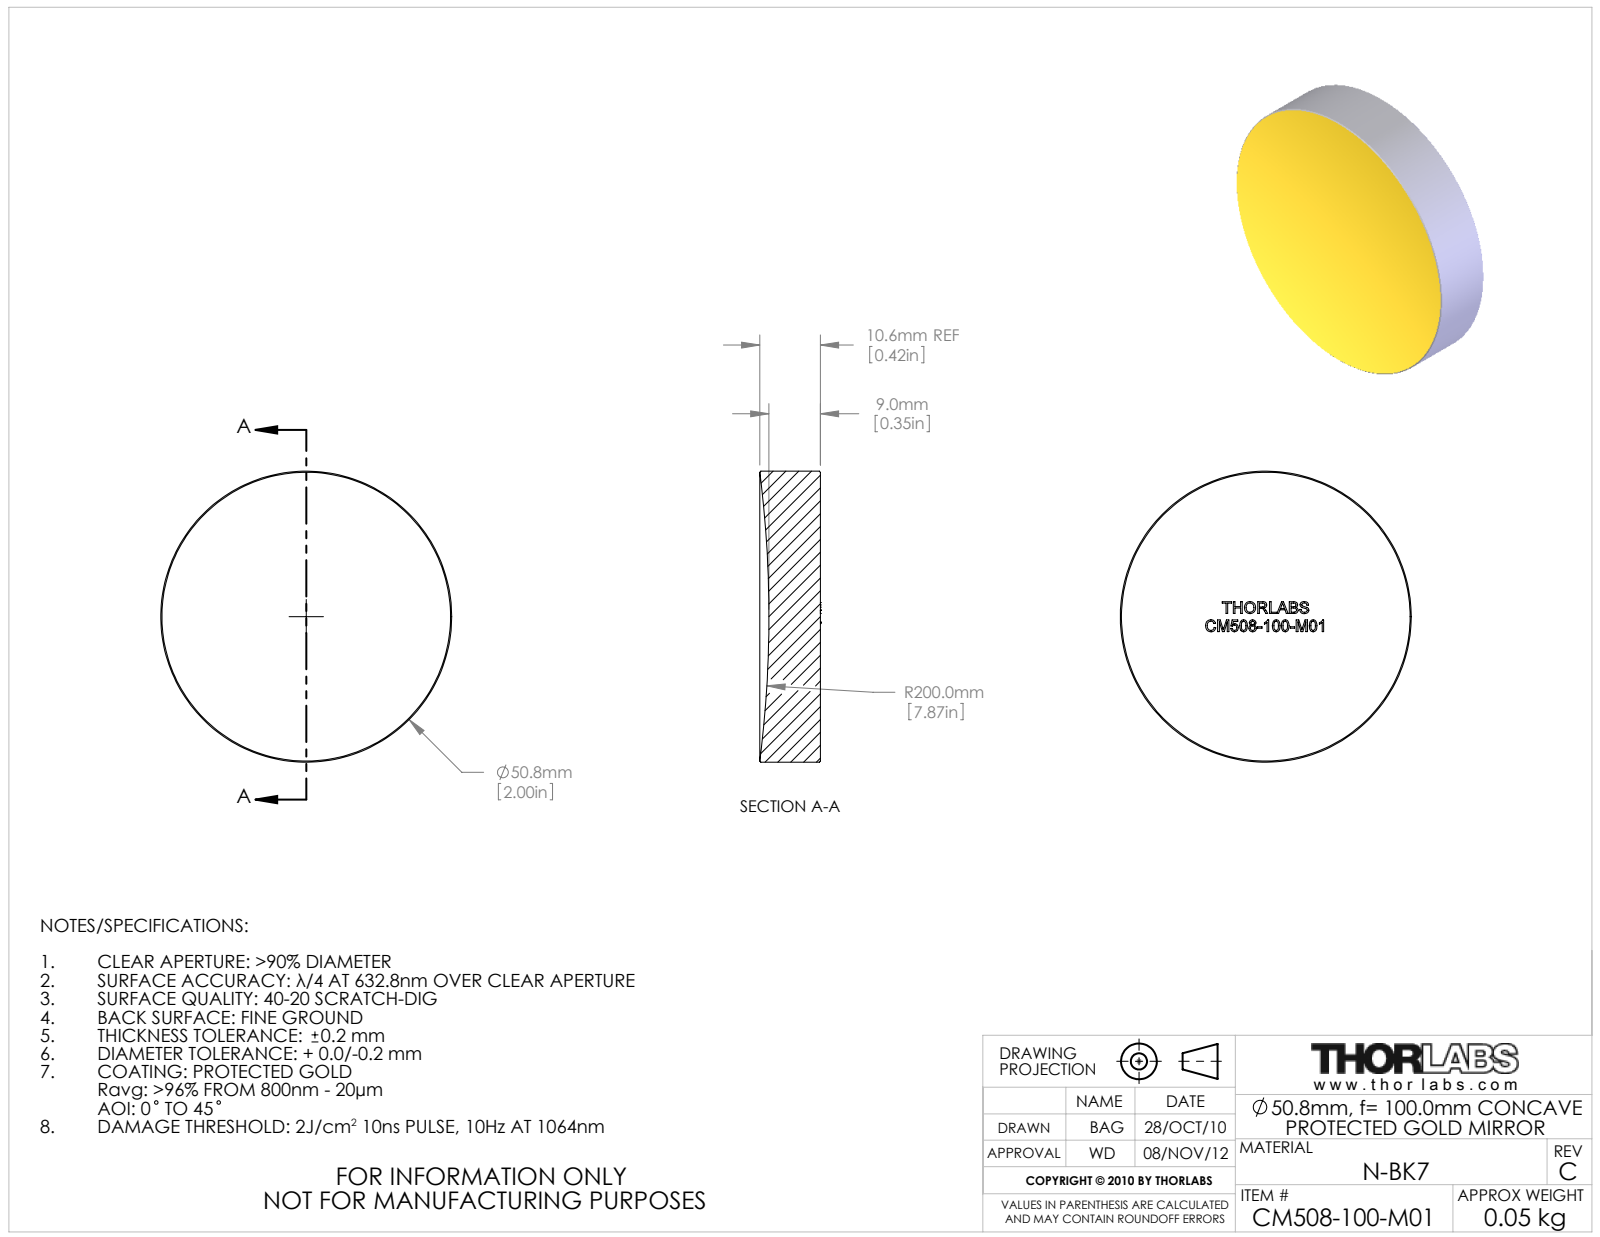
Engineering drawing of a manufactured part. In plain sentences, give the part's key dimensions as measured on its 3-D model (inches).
The part is named "17587-E0W". Its 3-D file was written by "SolidWorks 2009 (AUTOMOTIVE_DESIGN)". It is 1 solid with 276 faces: 145 planar, 2 cylindrical and 129 other. Overall it measures 2 by 2 by 0.417 inches. Its volume is 1.213 cubic inches and its surface area 8.86 square inches. Round bosses or shafts: 1 of diameter 2. The main face-to-face distances are 0.081, 0.125, 0.124, 0.218, 0.249, 0.038, 0.449, 0.541, 0.184, 0.433.
